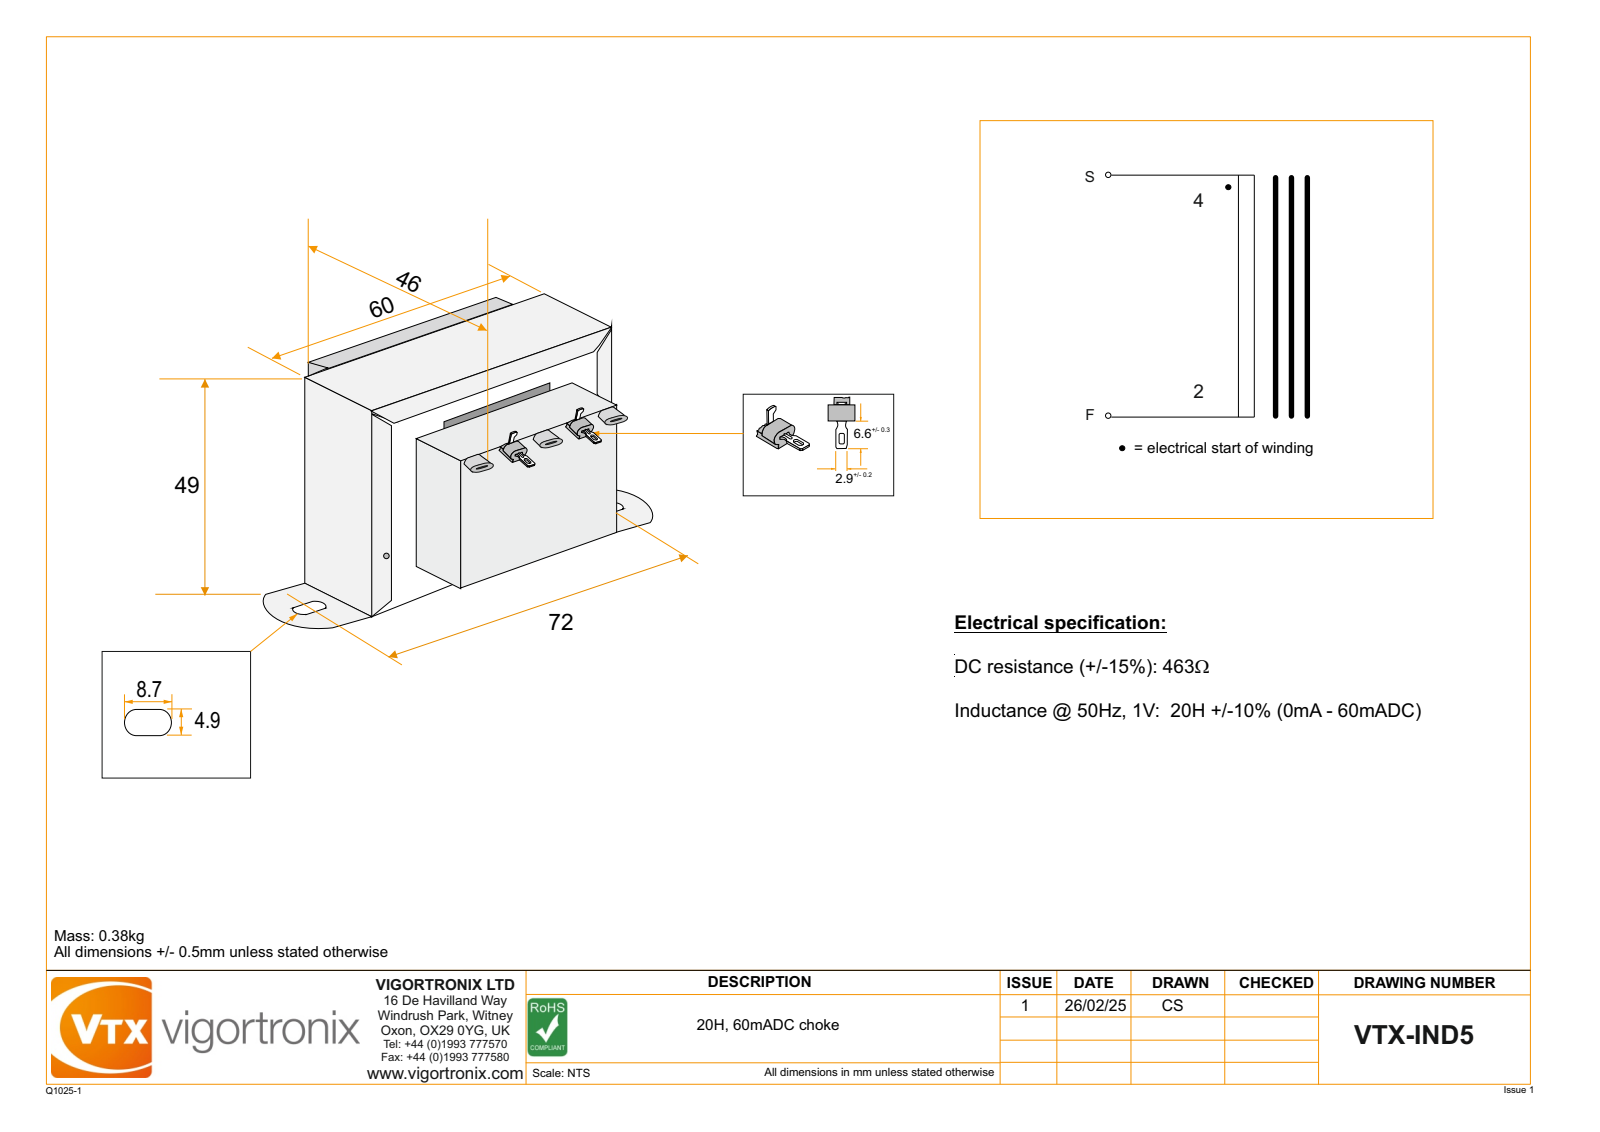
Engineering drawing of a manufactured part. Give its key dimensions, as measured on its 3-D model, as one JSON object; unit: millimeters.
{"part_name": "VTX-IND5; Terminal Pin 902 Bent; I UK35; Clamp EI UK35 (+3 more)", "step_written_by": "SolidWorks 2024 (AUTOMOTIVE_DESIGN)", "units": "millimeters", "bodies": {"solids": 101, "faces": 1511, "planar": 1364, "cylindrical": 135, "other": 12}, "overall_size": [90, 50.03, 49], "volume_mm3": 70336, "surface_area_mm2": 246119, "partial_cylinders_radius": [[1, 22], [1.5, 20], [0.63, 18], [0.1, 12], [1.8, 10], [0.25, 5], [2.45, 4], [7, 4]], "face_to_face_distances": [0.8, 1.6, 2.4, 3.2, 4, 4.8, 5.6, 6.4, 7.2, 8]}
